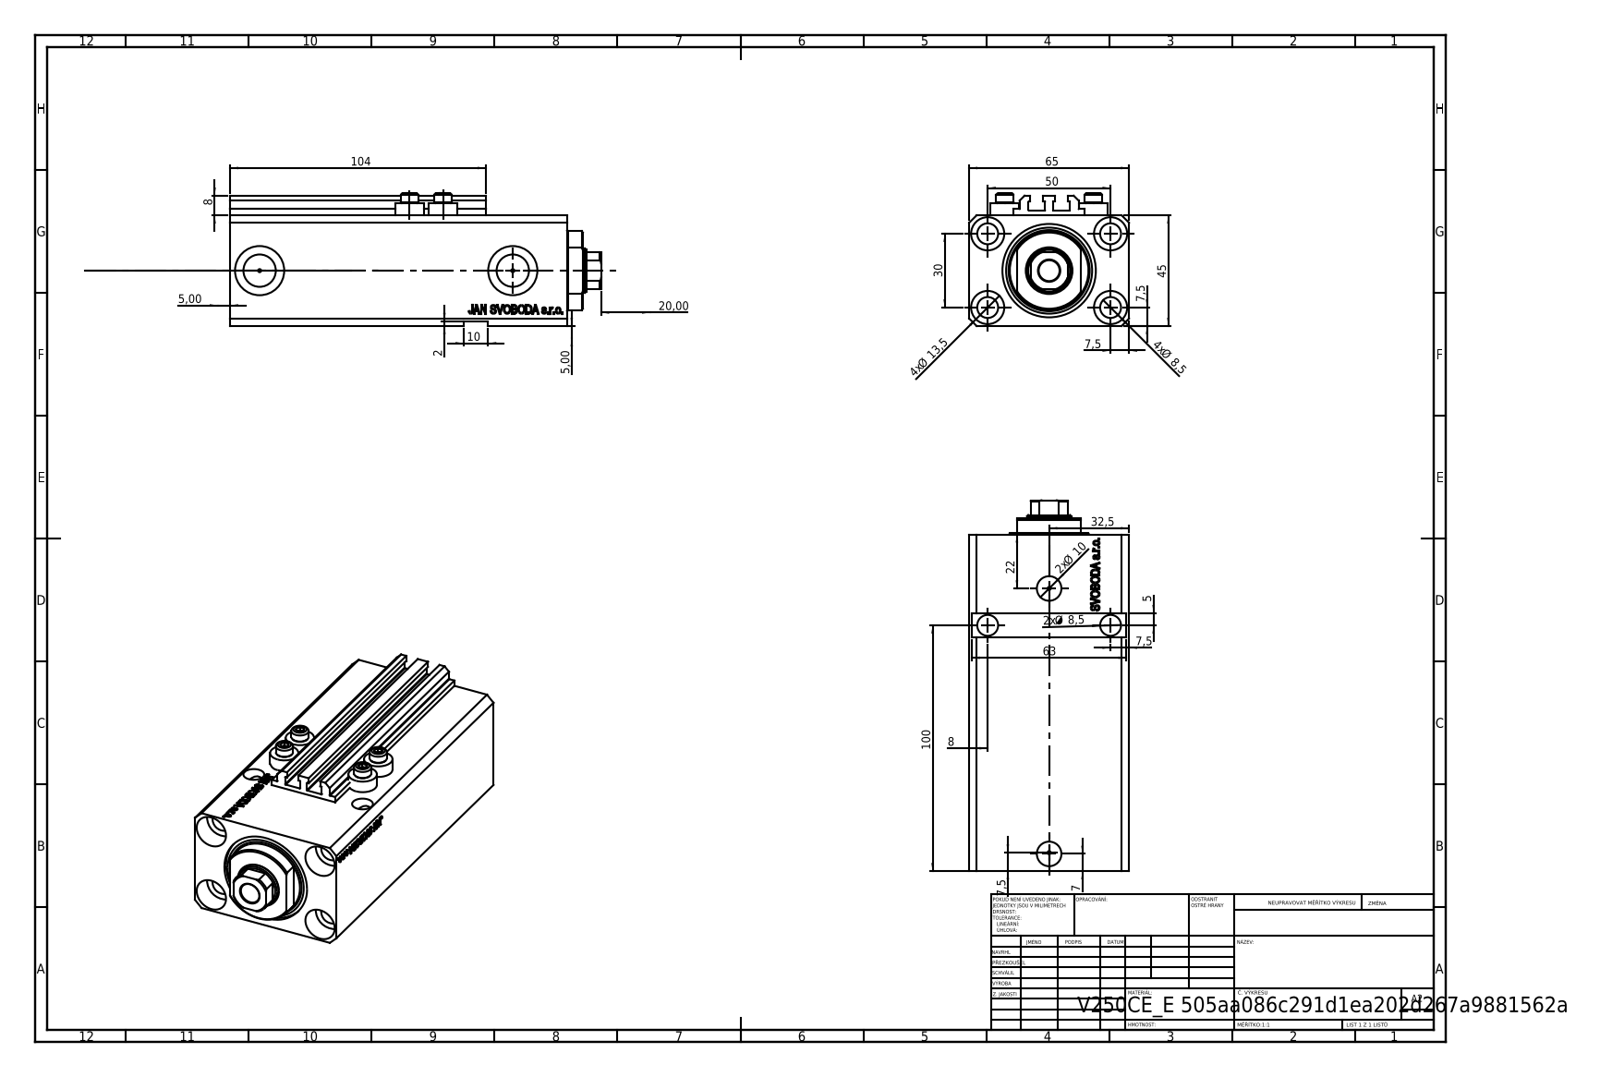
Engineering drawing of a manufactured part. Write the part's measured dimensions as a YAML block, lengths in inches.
part_name: "V250CE_VC_E; ALLEN BOLT V250CE; V250CE_C_VCP; V250CE_E_Body"
step_written_by: "SolidWorks 2019 (CONFIG_CONTROL_DESIGN)"
units: inches
bodies: {solids: 8, faces: 1067, planar: 511, cylindrical: 126, other: 430}
overall_size: [5.941, 2.559, 2.126]
volume: 21.6
surface_area: 146.7
round_holes:
  - {diameter: 0.335, count: 7}
  - {diameter: 0.049, count: 4}
  - {diameter: 0.157, count: 4}
  - {diameter: 0.531, count: 4}
  - {diameter: 0.394, count: 2}
  - {diameter: 0.518, count: 2}
  - {diameter: 0.787, count: 2}
  - {diameter: 0.709, count: 1}
  - {diameter: 0.984, count: 1}
  - {diameter: 1.496, count: 1}
round_bosses_or_shafts:
  - {diameter: 0.457, count: 4}
  - {diameter: 0.276, count: 4}
partial_cylinders:
  - {radius: 0.008, count: 10}
  - {radius: 0.335, count: 1}
  - {radius: 0.63, count: 1}
face_to_face_distances: [1.772, 2.559, 0.079, 1.85, 4.406, 0.098, 0.394, 5.394, 0.988, 0.272]
hole_center_spacings: [1.148, 1.969, 0.535, 0.595, 1.098, 1.181, 1.324, 1.417]
